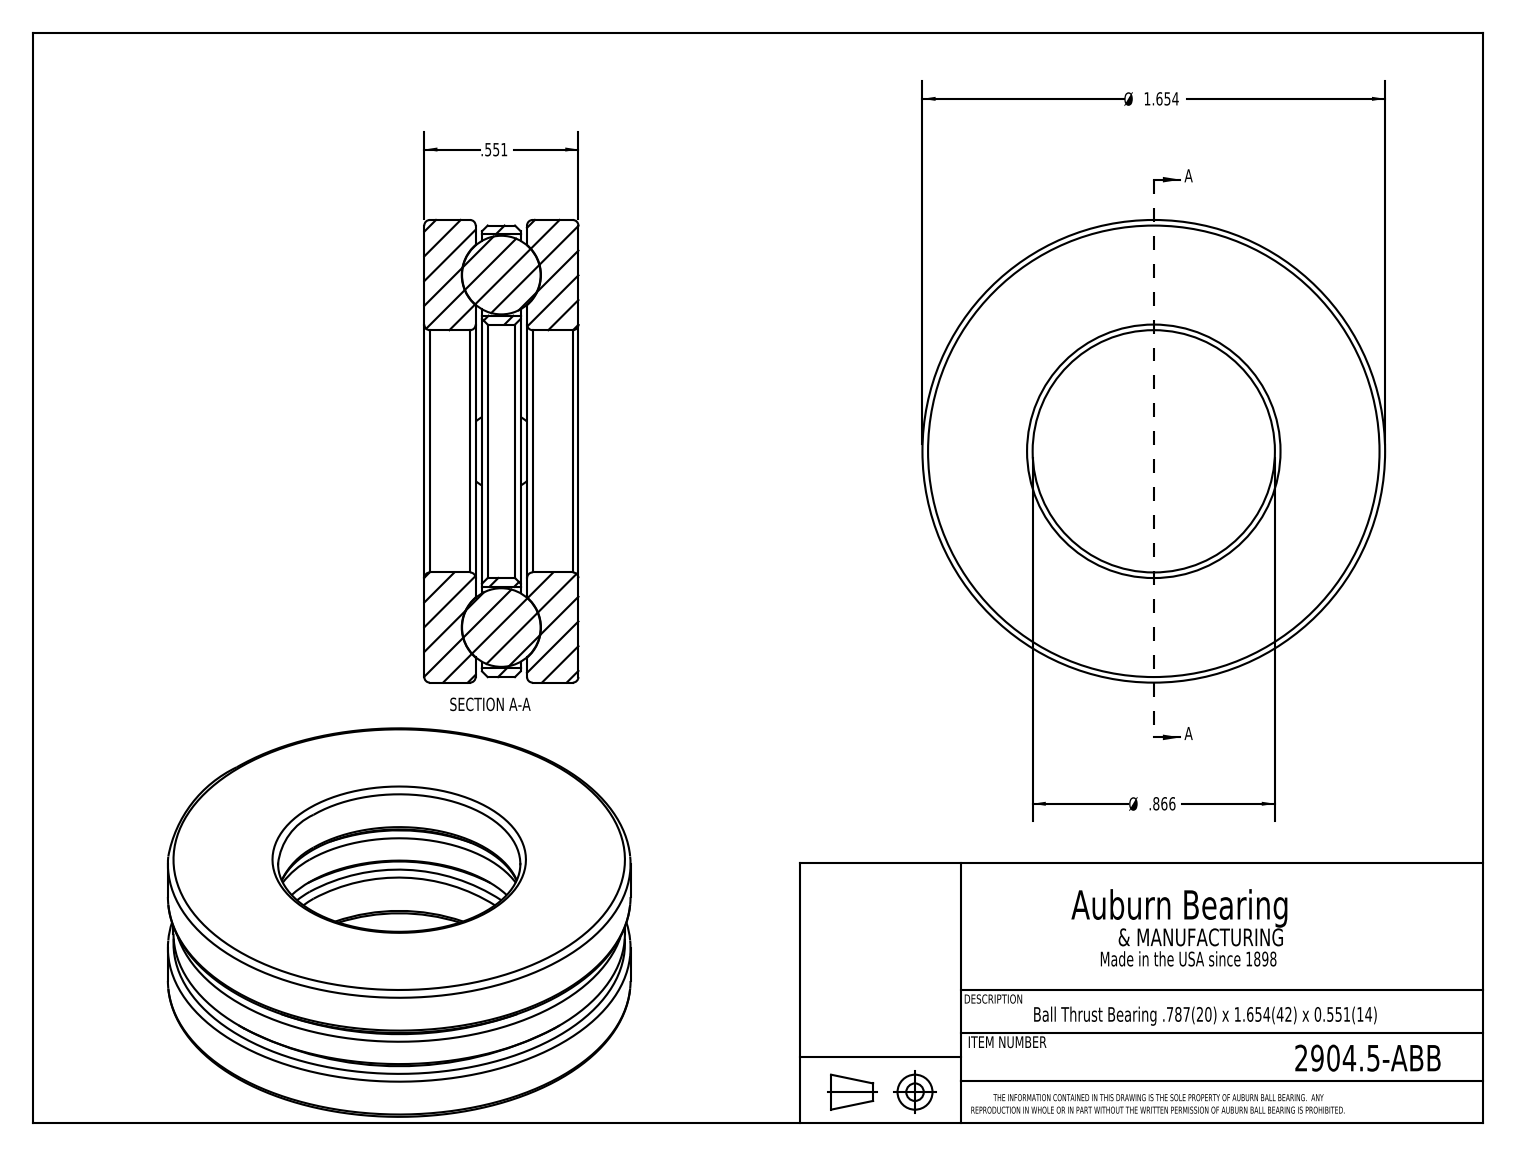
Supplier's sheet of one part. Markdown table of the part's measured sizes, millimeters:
| quantity | value |
| --- | --- |
| part name | 2904.5-ABB |
| STEP written by | SolidWorks 2017 (CONFIG_CONTROL_DESIGN) |
| units | millimeters |
| bodies | 7 solids, 36 faces (8 planar, 10 cylindrical, 18 other) |
| overall size | 42 × 42 × 14 |
| volume | 12 600 mm³ |
| surface area | 9 213 mm² |
| round holes (diameter × count) | 7.4 × 4, 20 × 1, 21 × 1 |
| round bosses / shafts (diameter × count) | 42 × 1, 41 × 1 |
| main face-to-face distances | 5.3, 8.7, 14, 4.7, 9.3, 0.6, 4.1, 3.5, 4.6 |
| hole center spacings | 15.5, 21.9, 31 |
